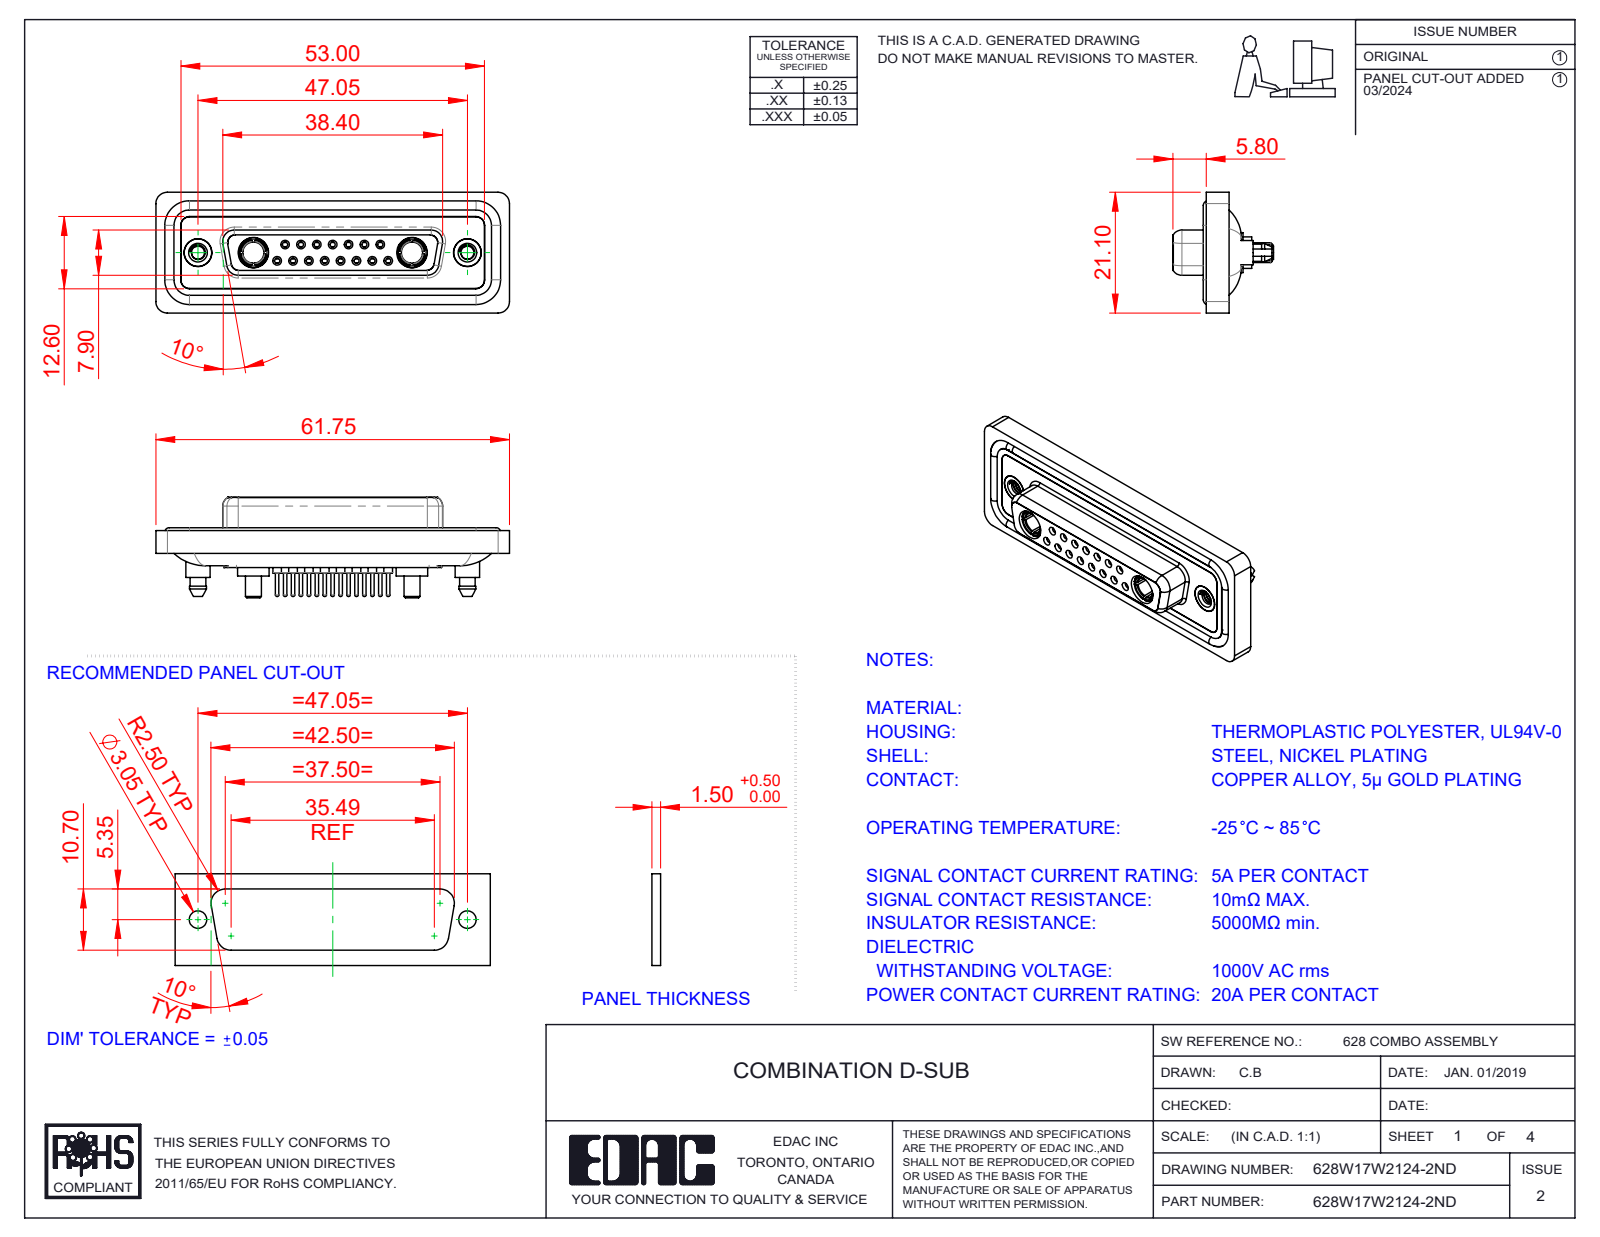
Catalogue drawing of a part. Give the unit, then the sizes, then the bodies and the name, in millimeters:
Units: millimetres
Overall size (bounding box): 61.75 × 21.1 × 17.55
Round holes (diameter × count): ⌀0.9 ×15, ⌀1.1 ×15, ⌀1.5 ×15, ⌀2 ×15, ⌀1.6 ×8, ⌀1.7 ×7, ⌀4.85 ×4, ⌀2.26 ×2, ⌀3.7 ×2, ⌀4 ×2, ⌀4.05 ×2, ⌀5 ×2
Round bosses / shafts (diameter × count): ⌀2.2 ×15, ⌀0.6 ×15, ⌀1.6 ×11, ⌀5.5 ×2, ⌀5.4 ×2, ⌀5.2 ×2, ⌀4.96 ×2, ⌀4.95 ×2
Partial cylindrical surfaces — rounded edges, fillets, slot ends (radius × count): R1.5 ×24, R2 ×18, R1.6 ×10, R1.35 ×8, R0.25 ×4, R0.5 ×4, R0.6 ×4, R0.65 ×4
Main face-to-face distances: 0.4, 1.8, 7.45, 5.65, 6.6, 0.5, 7.05, 1.6, 2.9, 1.1
Hole centre spacings: 3.16, 2.77, 8.31, 5.54, 5.03, 5.04, 7.49, 11.08
Volume: 8 459 mm³ · Surface area: 14 194 mm²
Bodies: 26 solids, 1425 faces (404 planar, 567 cylindrical, 454 other)
Part name (STEP PRODUCT): 628Combo Shell Front_25 Contacts; 628Combo Contact Row 1_24; 628Combo Contact Row 2_24; 628Combo Shell Rear_25 Contacts (+5 more)
STEP written by: SolidWorks 2023 (CONFIG_CONTROL_DESIGN)
